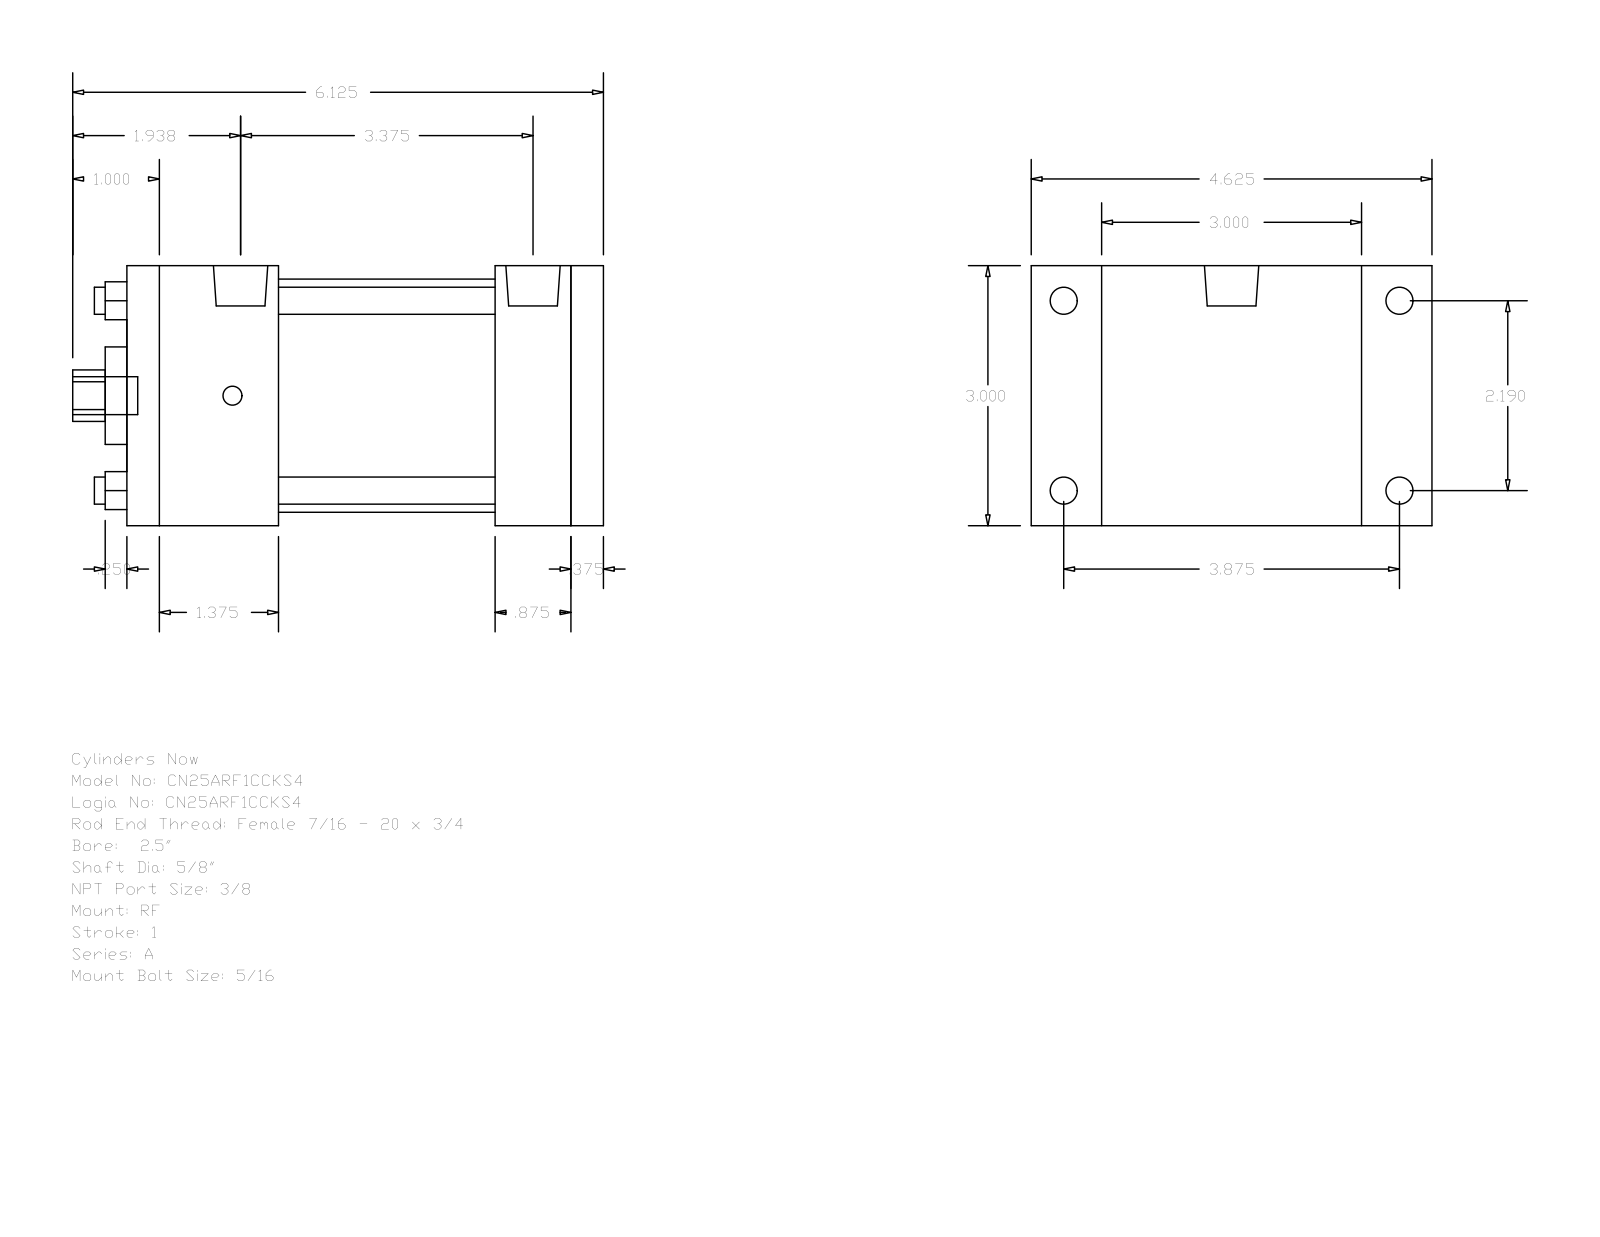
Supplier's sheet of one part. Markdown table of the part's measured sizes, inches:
| quantity | value |
| --- | --- |
| part name | A_RF__0250_0.625 |
| STEP written by | GSSL Pune (CONFIG_CONTROL_DESIGN) |
| units | inches |
| bodies | 0 solids, 92 faces (64 planar, 28 cylindrical, 0 other) |
| overall size | 6.125 × 4.625 × 3 |
| round holes (diameter × count) | 0.313 × 4, 0.625 × 1, 1.125 × 1, 2.69 × 1 |
| round bosses / shafts (diameter × count) | 0.313 × 4, 0.219 × 4, 0.627 × 2, 0.437 × 1 |
| partial cylindrical surfaces (radius × count) | 0.297 × 1 |
| main face-to-face distances | 3, 5.5, 0.375, 5.125, 1.75, 3.75, 4.25, 2.5, 3.375, 0.875 |
| hole center spacings | 1.548, 2.19, 3.097 |
